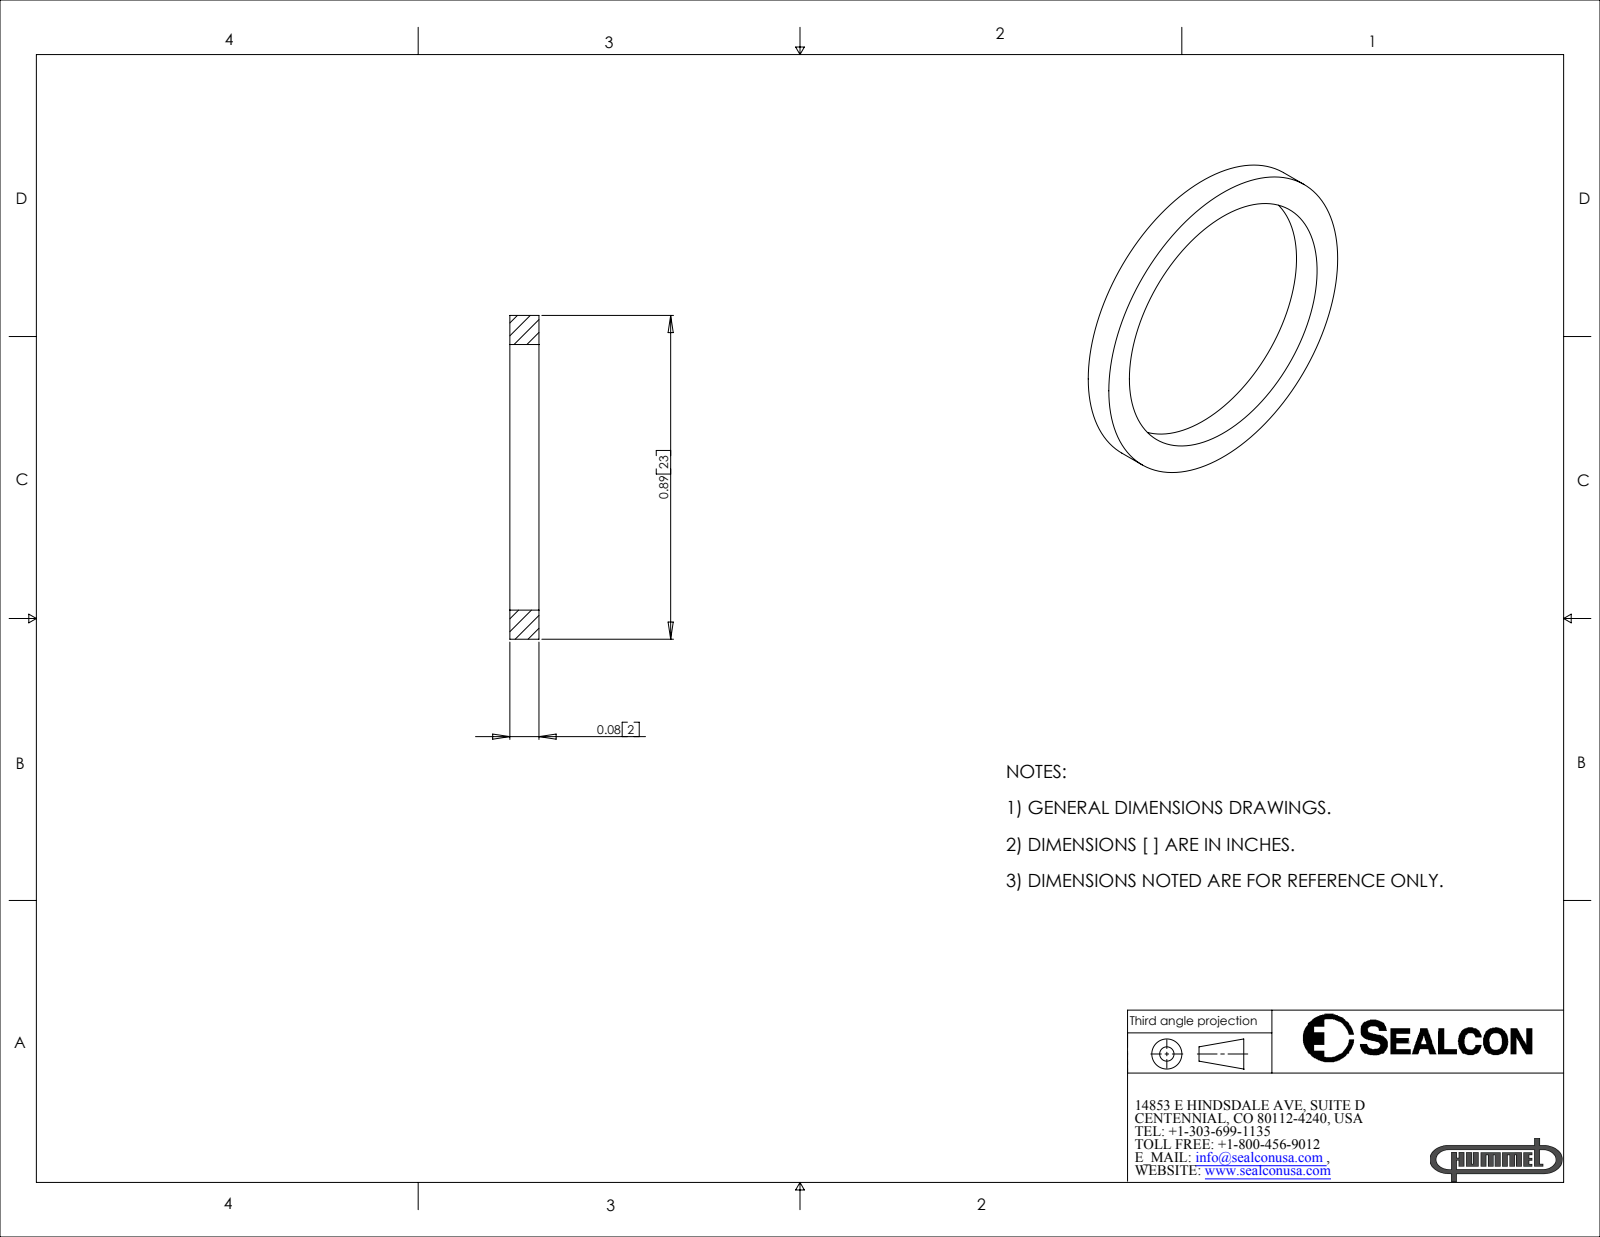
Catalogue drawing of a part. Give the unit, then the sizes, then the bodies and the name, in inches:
Units: inches
Overall size (bounding box): 0.89 × 0.89 × 0.08
Round holes (diameter × count): ⌀0.73 ×1
Round bosses / shafts (diameter × count): ⌀0.89 ×1
Main face-to-face distances: 0.08
Volume: 0.016 in³ · Surface area: 0.814 in²
Bodies: 1 solid, 6 faces (2 planar, 4 cylindrical, 0 other)
Part name (STEP PRODUCT): SR-11-VT
STEP written by: SolidWorks 2007 (CONFIG_CONTROL_DESIGN)
